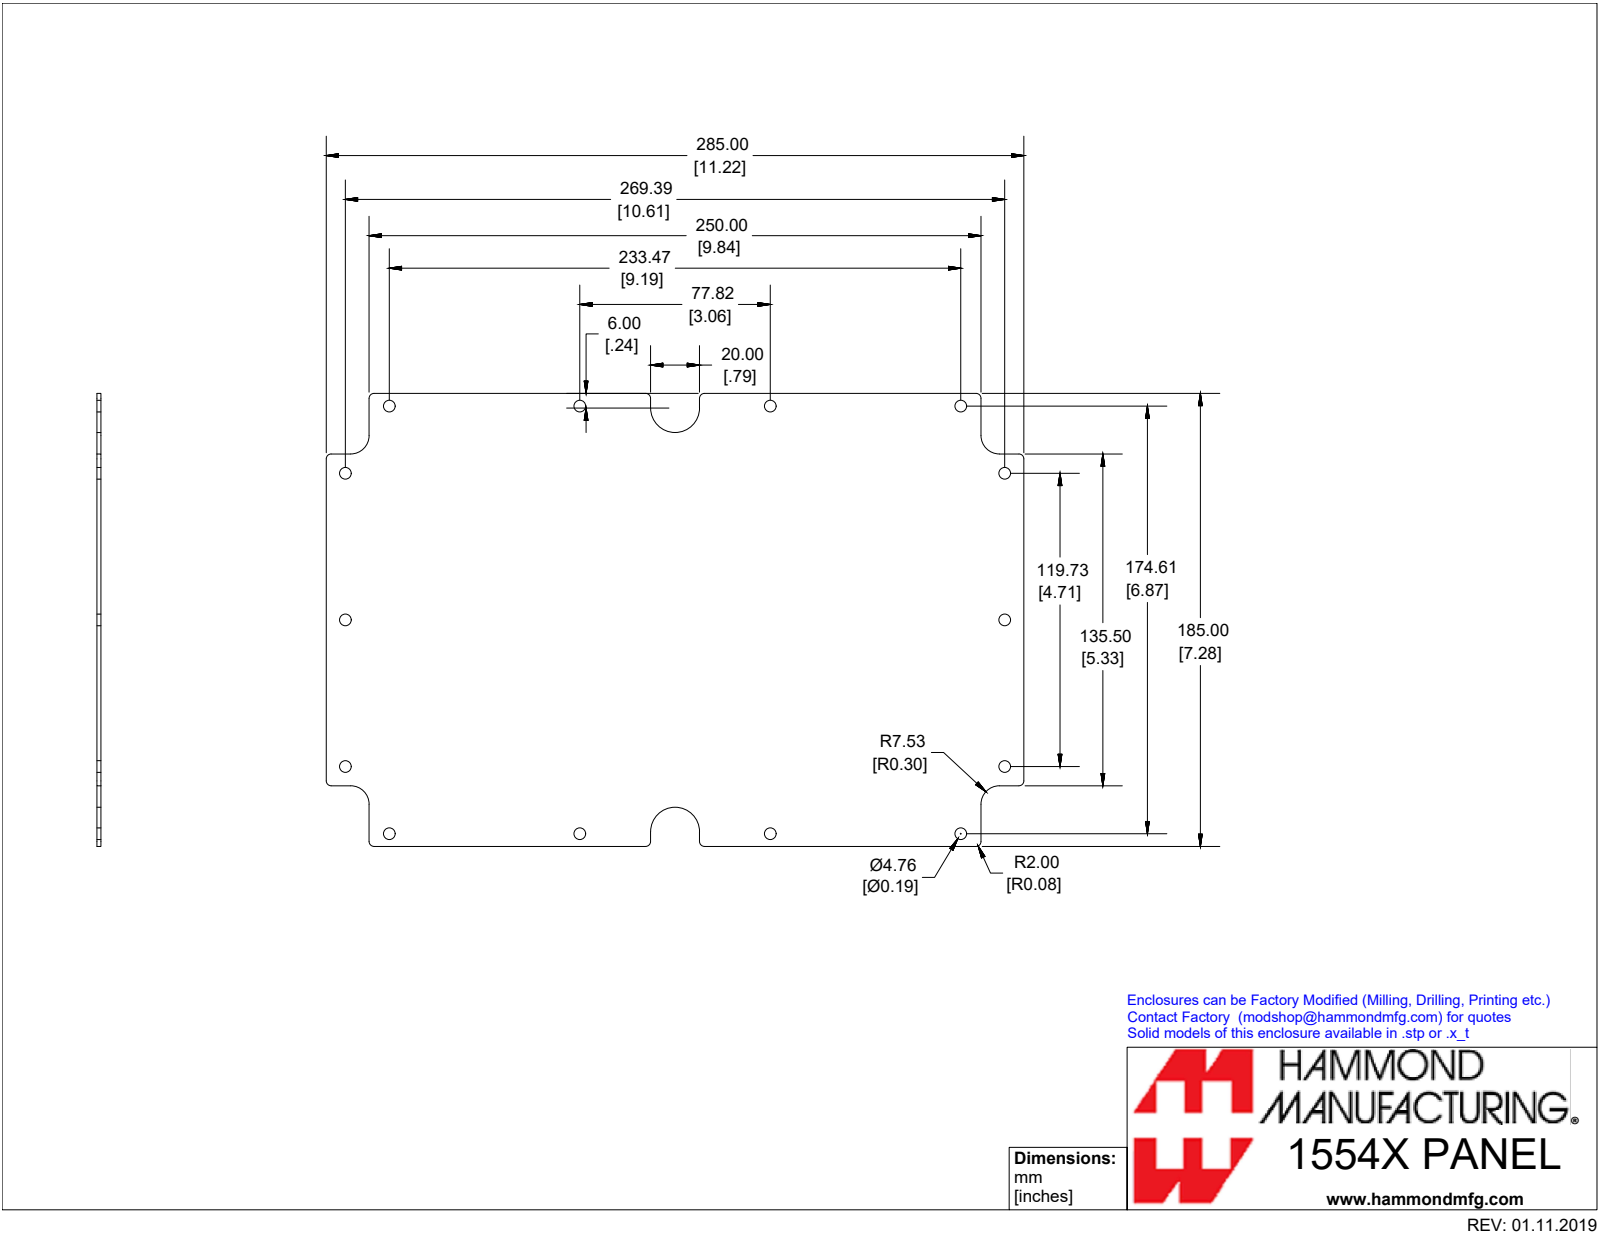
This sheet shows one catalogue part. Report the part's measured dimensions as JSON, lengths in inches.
{"part_name": "1554XPL", "step_written_by": "SolidWorks 2019 (CONFIG_CONTROL_DESIGN)", "units": "inches", "bodies": {"solids": 1, "faces": 52, "planar": 20, "cylindrical": 32, "other": 0}, "overall_size": [11.22, 7.283, 0.064], "volume_in3": 4.983, "surface_area_in2": 158.7, "round_holes": [[0.187, 14]], "partial_cylinders_radius": [[0.079, 12], [0.296, 4], [0.394, 2]], "face_to_face_distances": [0.064, 7.283, 11.22, 0.689, 10.531, 0.974, 6.309, 9.843, 5.217, 6.004], "hole_center_spacings": [3.064, 7.527, 1.291, 2.357, 3.509, 3.923, 5.103, 5.837]}
